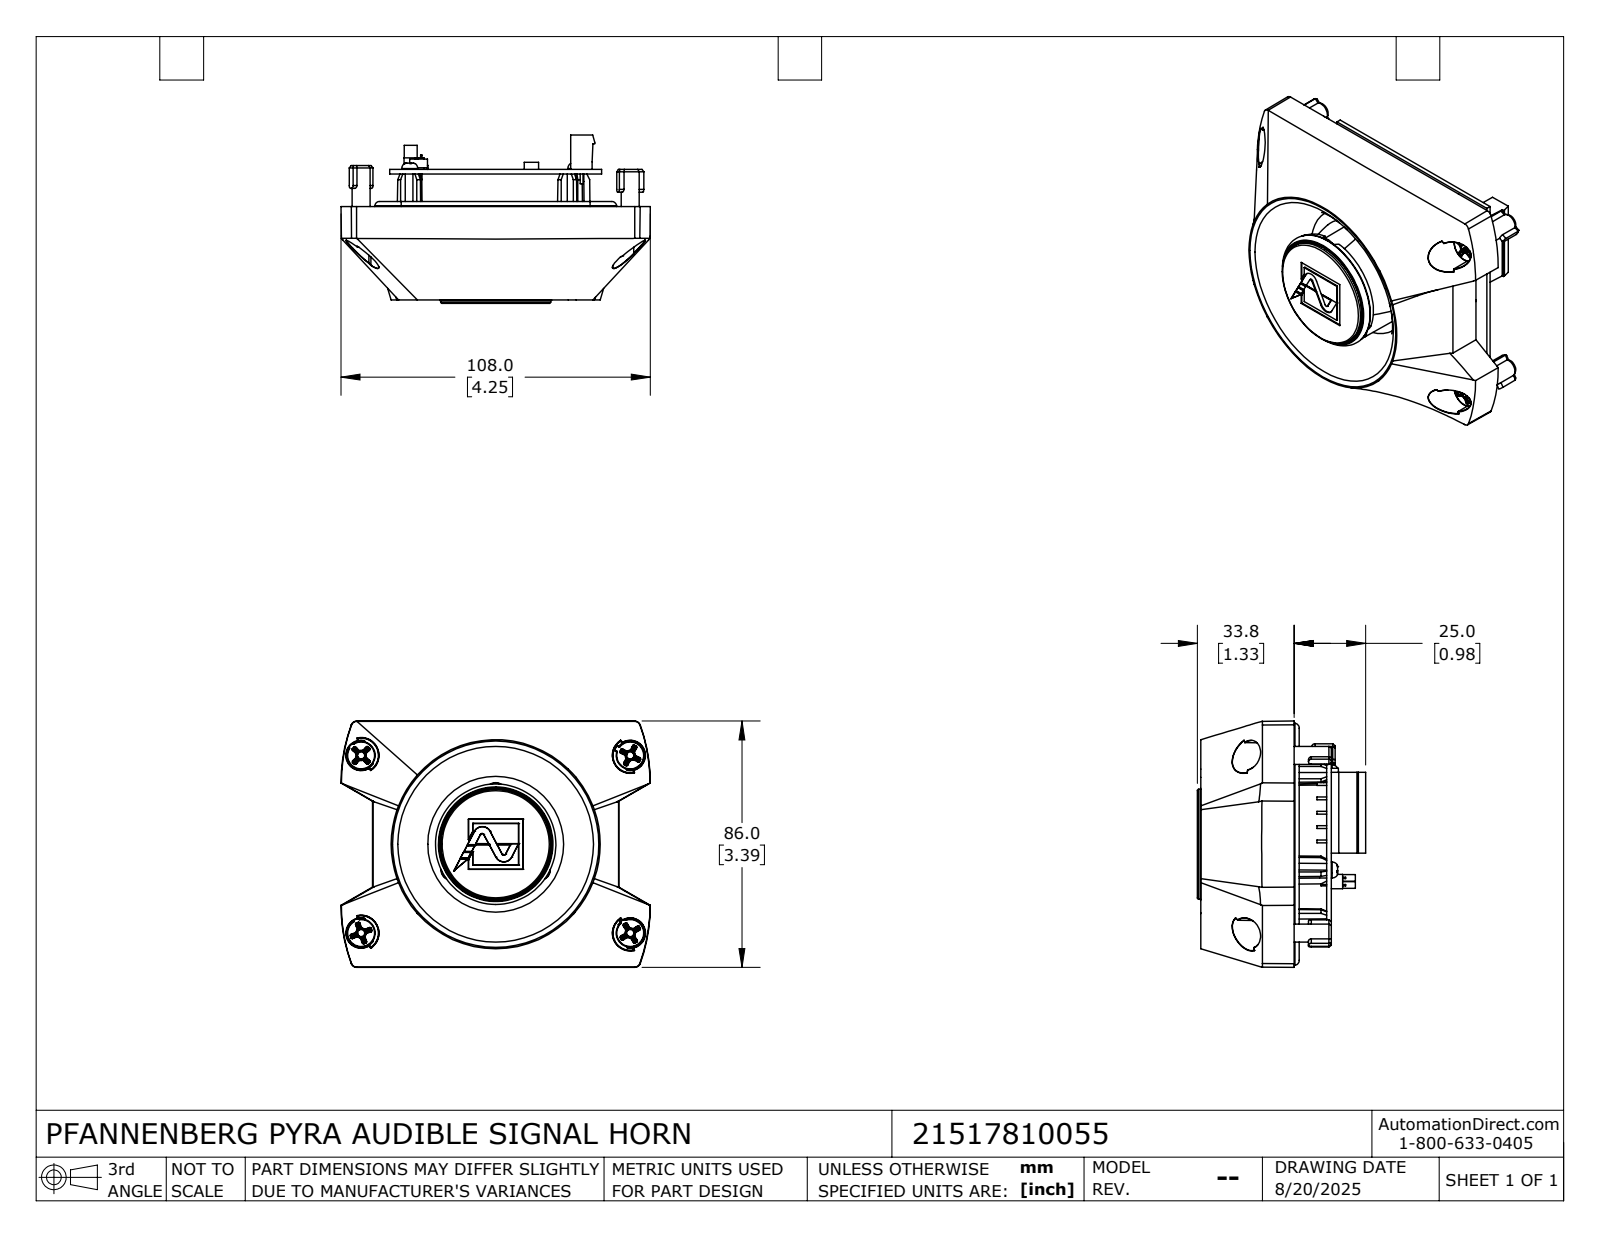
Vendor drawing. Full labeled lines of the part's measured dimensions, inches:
Part name (STEP PRODUCT): 21517810055
STEP written by: SolidWorks 2024 (CONFIG_CONTROL_DESIGN)
Units: inches
Bodies: 9 solids, 1957 faces (948 planar, 243 cylindrical, 766 other)
Overall size (bounding box): 4.252 × 3.386 × 2.314
Volume: 13.13 in³ · Surface area: 81.76 in²
Round holes (diameter × count): ⌀0.039 ×2, ⌀0.059 ×2, ⌀0.118 ×2, ⌀0.098 ×1
Round bosses / shafts (diameter × count): ⌀0.11 ×5, ⌀0.386 ×4, ⌀0.248 ×4, ⌀0.22 ×2, ⌀0.114 ×2, ⌀1.656 ×1, ⌀0.091 ×1
Partial cylindrical surfaces — rounded edges, fillets, slot ends (radius × count): R0.008 ×94, R0.118 ×5, R0.039 ×4, R0.069 ×4, R0.201 ×4, R0.004 ×2, R0.232 ×2, R0.394 ×2
Main face-to-face distances: 0.511, 0.063, 0.448, 1.331, 1.841, 1.778, 0.079, 3.386, 0.768, 0.11
Hole centre spacings: 0.197, 0.494, 0.677, 0.819, 0.872, 1.013, 1.303, 1.344
